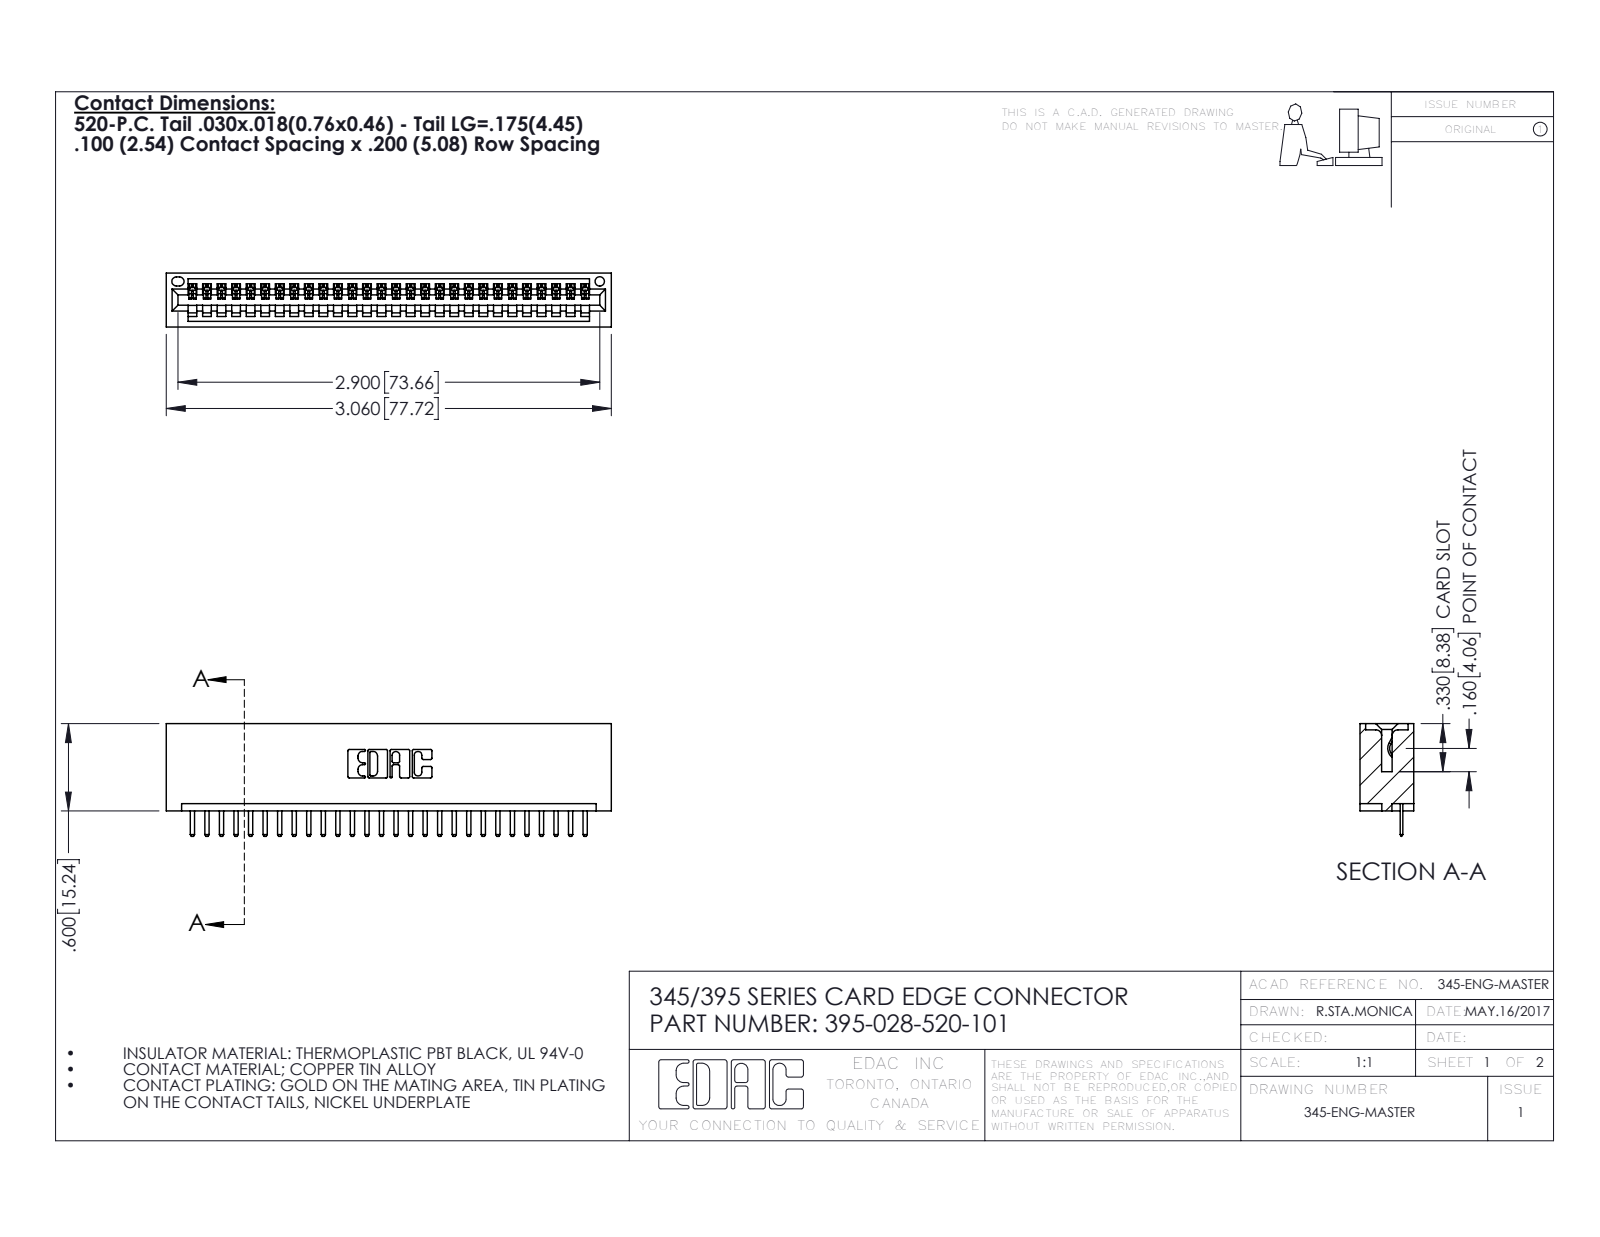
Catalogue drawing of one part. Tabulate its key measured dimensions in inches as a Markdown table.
| quantity | value |
| --- | --- |
| part name | 345-292-001_345-293-120; 345 Part_No Mounting Lugs; 395-028-520-101 |
| STEP written by | SolidWorks 2016 (CONFIG_CONTROL_DESIGN) |
| units | inches |
| bodies | 29 solids, 1854 faces (1252 planar, 602 cylindrical, 0 other) |
| overall size | 3.06 × 0.775 × 0.37 |
| volume | 0.474 in³ |
| surface area | 15.6 in² |
| round holes (diameter × count) | 0.064 × 1 |
| partial cylindrical surfaces (radius × count) | 0.01 × 58, 0.006 × 56, 0.01 × 22, 0.007 × 6, 0.031 × 6, 0.026 × 3, 0.031 × 2, 0.04 × 2 |
| main face-to-face distances | 0.298, 0.072, 0.37, 0.2, 0.098, 0.272, 0.025, 0.225, 0.072, 0.149 |
